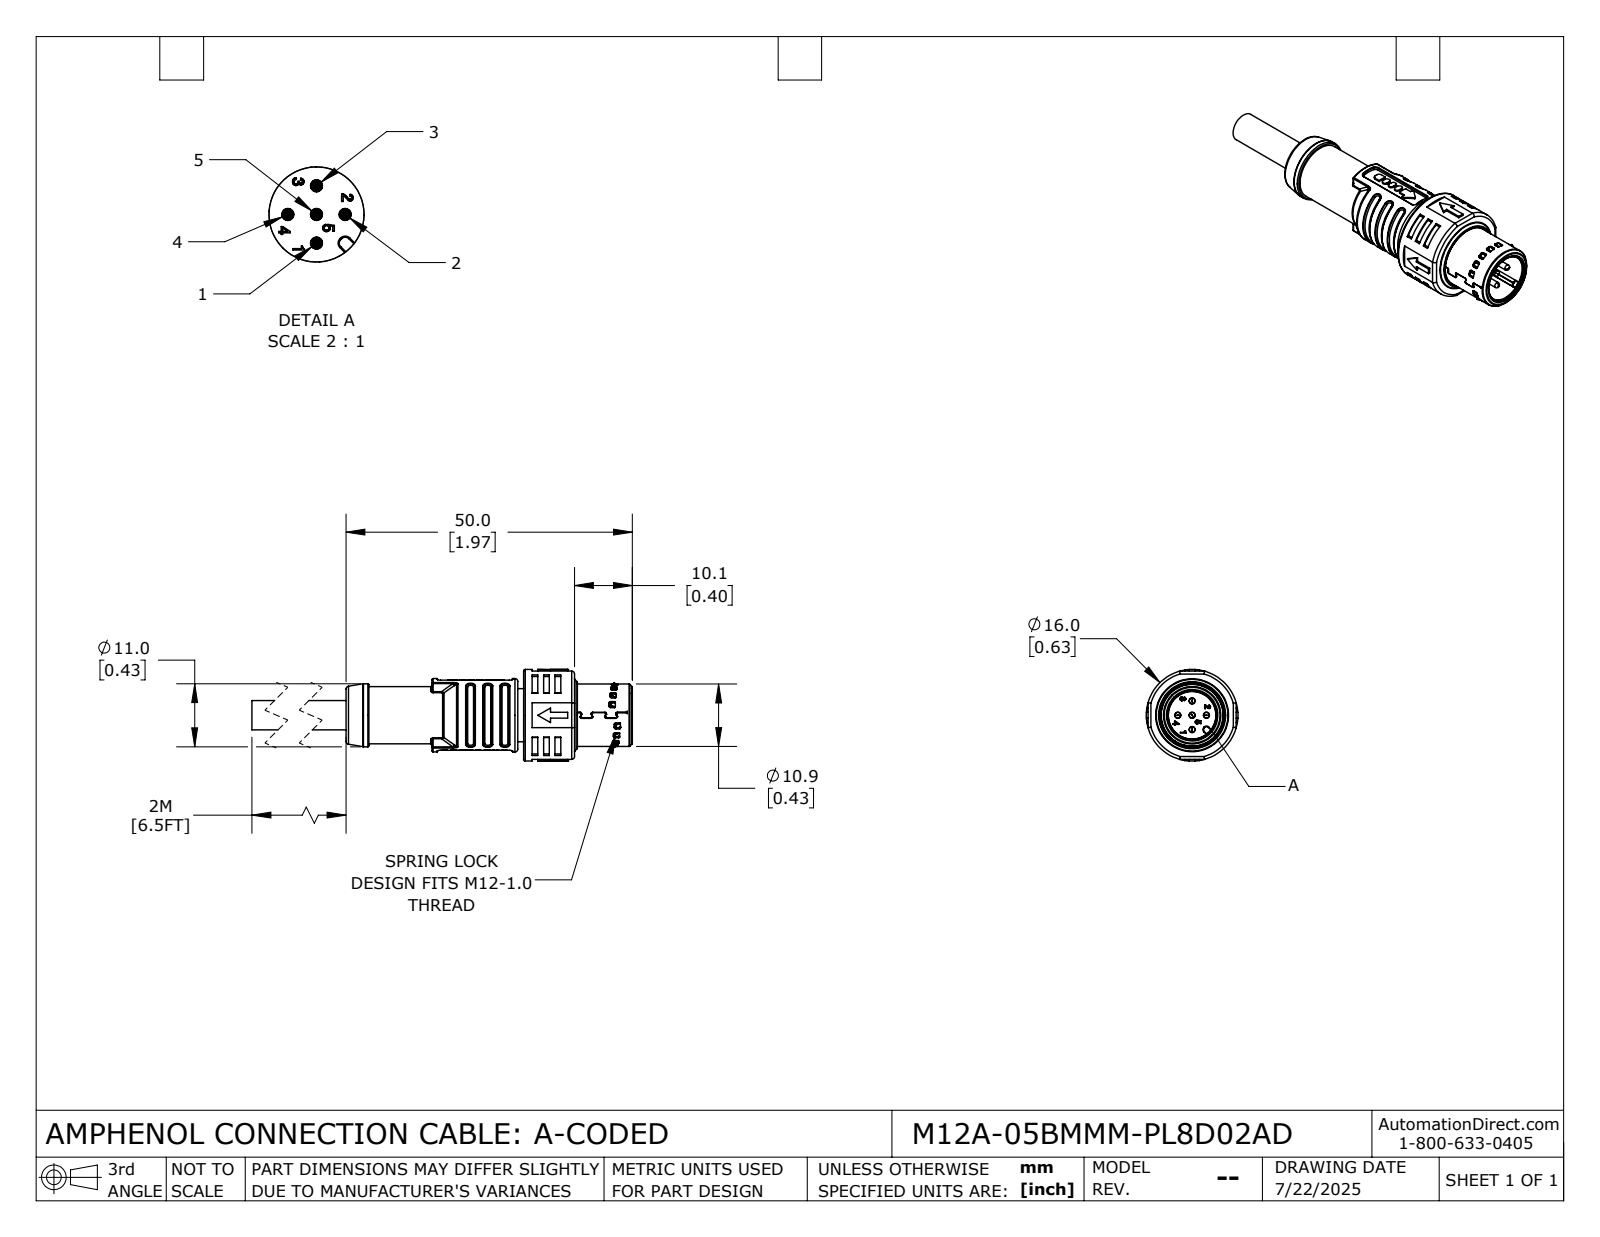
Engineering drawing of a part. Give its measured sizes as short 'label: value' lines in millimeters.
name: M12A-05BMMM-PL8D02AD
written by: SolidWorks 2024 (CONFIG_CONTROL_DESIGN)
unit: mm
bodies: 1 solid, 2230 faces (1085 planar, 648 cylindrical, 497 other)
size: 65 × 16 × 16
volume: 5 076 mm³; area: 5 586 mm²
holes: 5× ⌀1.05, 1× ⌀8.3, 1× ⌀9, 1× ⌀10.15, 1× ⌀10.5, 1× ⌀10.9, 1× ⌀11.5, 1× ⌀11.8, 1× ⌀14.2
bosses: 5× ⌀1, 1× ⌀16, 1× ⌀14.1, 1× ⌀12.8, 1× ⌀12.4, 1× ⌀11, 1× ⌀10.45, 1× ⌀10.4
rounds: 114× R0.2, 66× R0.25, 64× R0.3, 44× R0.15, 38× R0.5, 12× R0.13, 11× R0.7, 10× R0.1
face distances: 1, 10.1, 8.9, 8.6, 2.5, 30, 1.5, 1.2, 32.5, 15.4
hole spacings: 2.5, 3.54, 5
